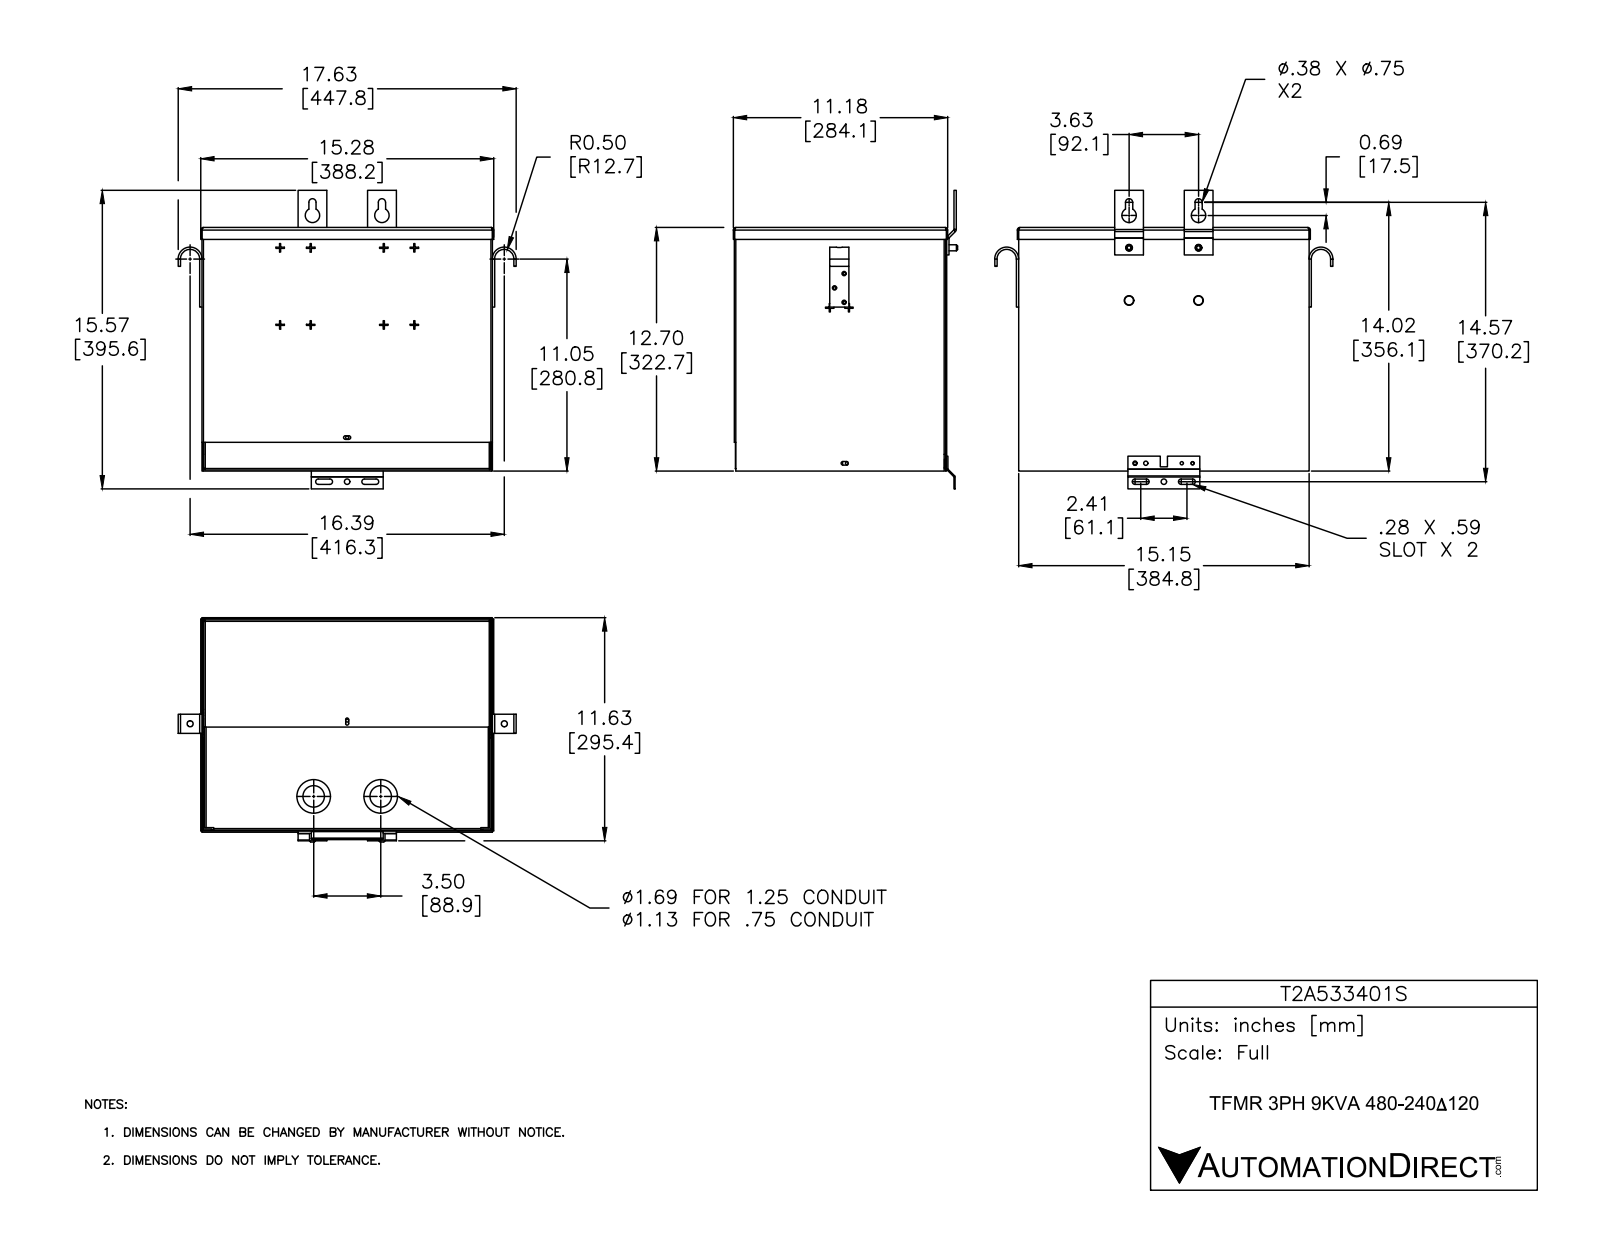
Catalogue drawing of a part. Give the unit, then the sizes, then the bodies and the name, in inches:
Units: inches
Overall size (bounding box): 17.63 × 15.574 × 11.697
Round holes (diameter × count): ⌀0.16 ×5, ⌀0.313 ×4, ⌀0.172 ×2, ⌀0.219 ×2, ⌀0.281 ×2, ⌀0.344 ×2, ⌀0.75 ×2, ⌀1.125 ×2, ⌀1.75 ×2, ⌀0.173 ×1, ⌀0.187 ×1
Round bosses / shafts (diameter × count): ⌀1.81 ×2, ⌀1.185 ×2, ⌀0.312 ×2
Partial cylindrical surfaces — rounded edges, fillets, slot ends (radius × count): R0.015 ×12, R0.075 ×12, R0.094 ×8, R0.075 ×4, R0.135 ×4, R0.141 ×4, R0.02 ×2, R0.03 ×2
Main face-to-face distances: 0.06, 11.02, 15.09, 10.96, 11.08, 12.52, 12.587, 0.067, 15.15, 15.03
Hole centre spacings: 0.563, 1.342, 1.638, 1.688, 1.781, 2.014, 2.437, 3.625
Volume: 66.19 in³ · Surface area: 2 202 in²
Bodies: 12 solids, 707 faces (499 planar, 138 cylindrical, 70 other)
Part name (STEP PRODUCT): T2A533401S
STEP written by: SolidWorks 2015 (AUTOMOTIVE_DESIGN)
